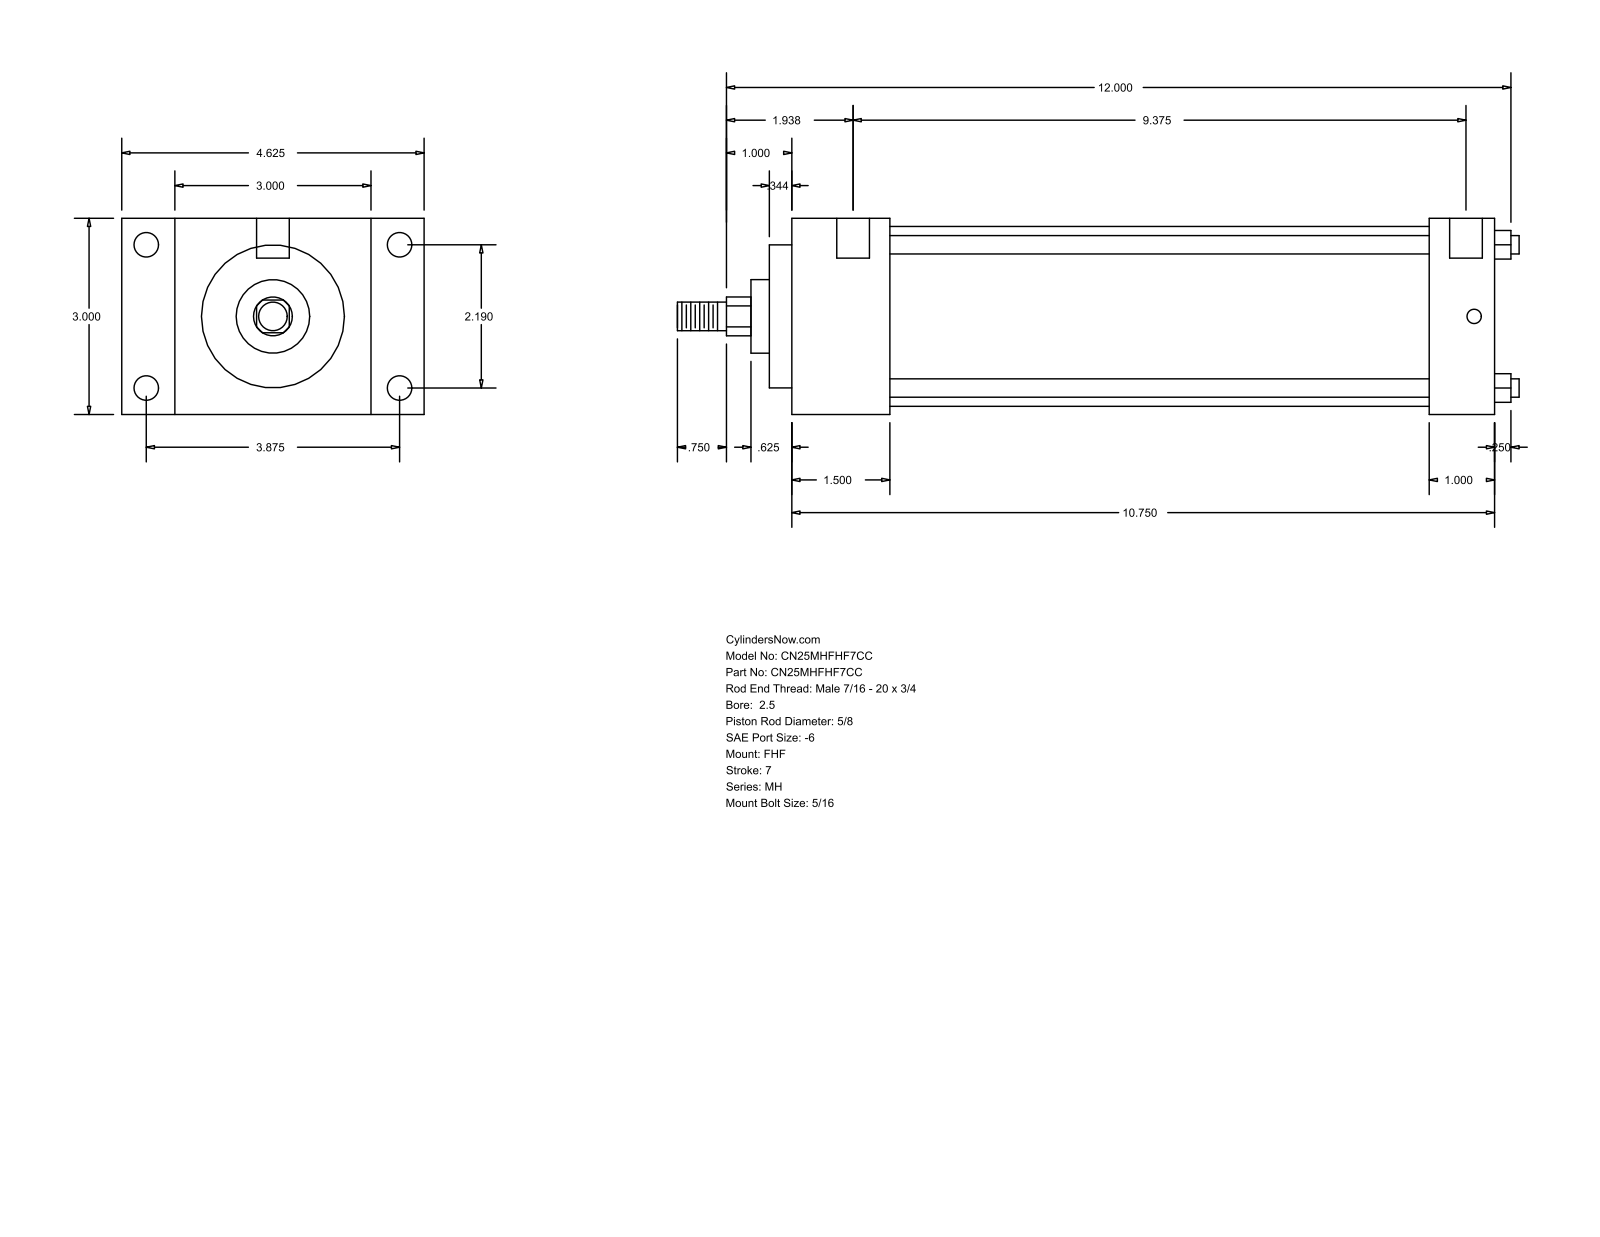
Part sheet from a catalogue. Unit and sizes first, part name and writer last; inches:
Units: inches
Overall size (bounding box): 12.875 × 4.625 × 3
Round holes (diameter × count): ⌀0.219 ×4, ⌀0.375 ×4, ⌀0.5 ×2
Round bosses / shafts (diameter × count): ⌀0.281 ×4, ⌀2.75 ×1, ⌀2.187 ×1, ⌀1.125 ×1, ⌀0.625 ×1, ⌀0.437 ×1
Partial cylindrical surfaces — rounded edges, fillets, slot ends (radius × count): R0.297 ×1
Main face-to-face distances: 3, 10.75, 1.5, 9.25, 0.813, 3.813, 4.625, 1, 9.75, 8.25
Hole centre spacings: 2.19, 3.875, 4.451, 9.687, 0.125, 0.187, 9.375, 9.5
Bodies: 0 solids, 90 faces (61 planar, 29 cylindrical, 0 other)
Part name (STEP PRODUCT): MH_FHF__0250_0.625
STEP written by: GSSL Pune (CONFIG_CONTROL_DESIGN)
